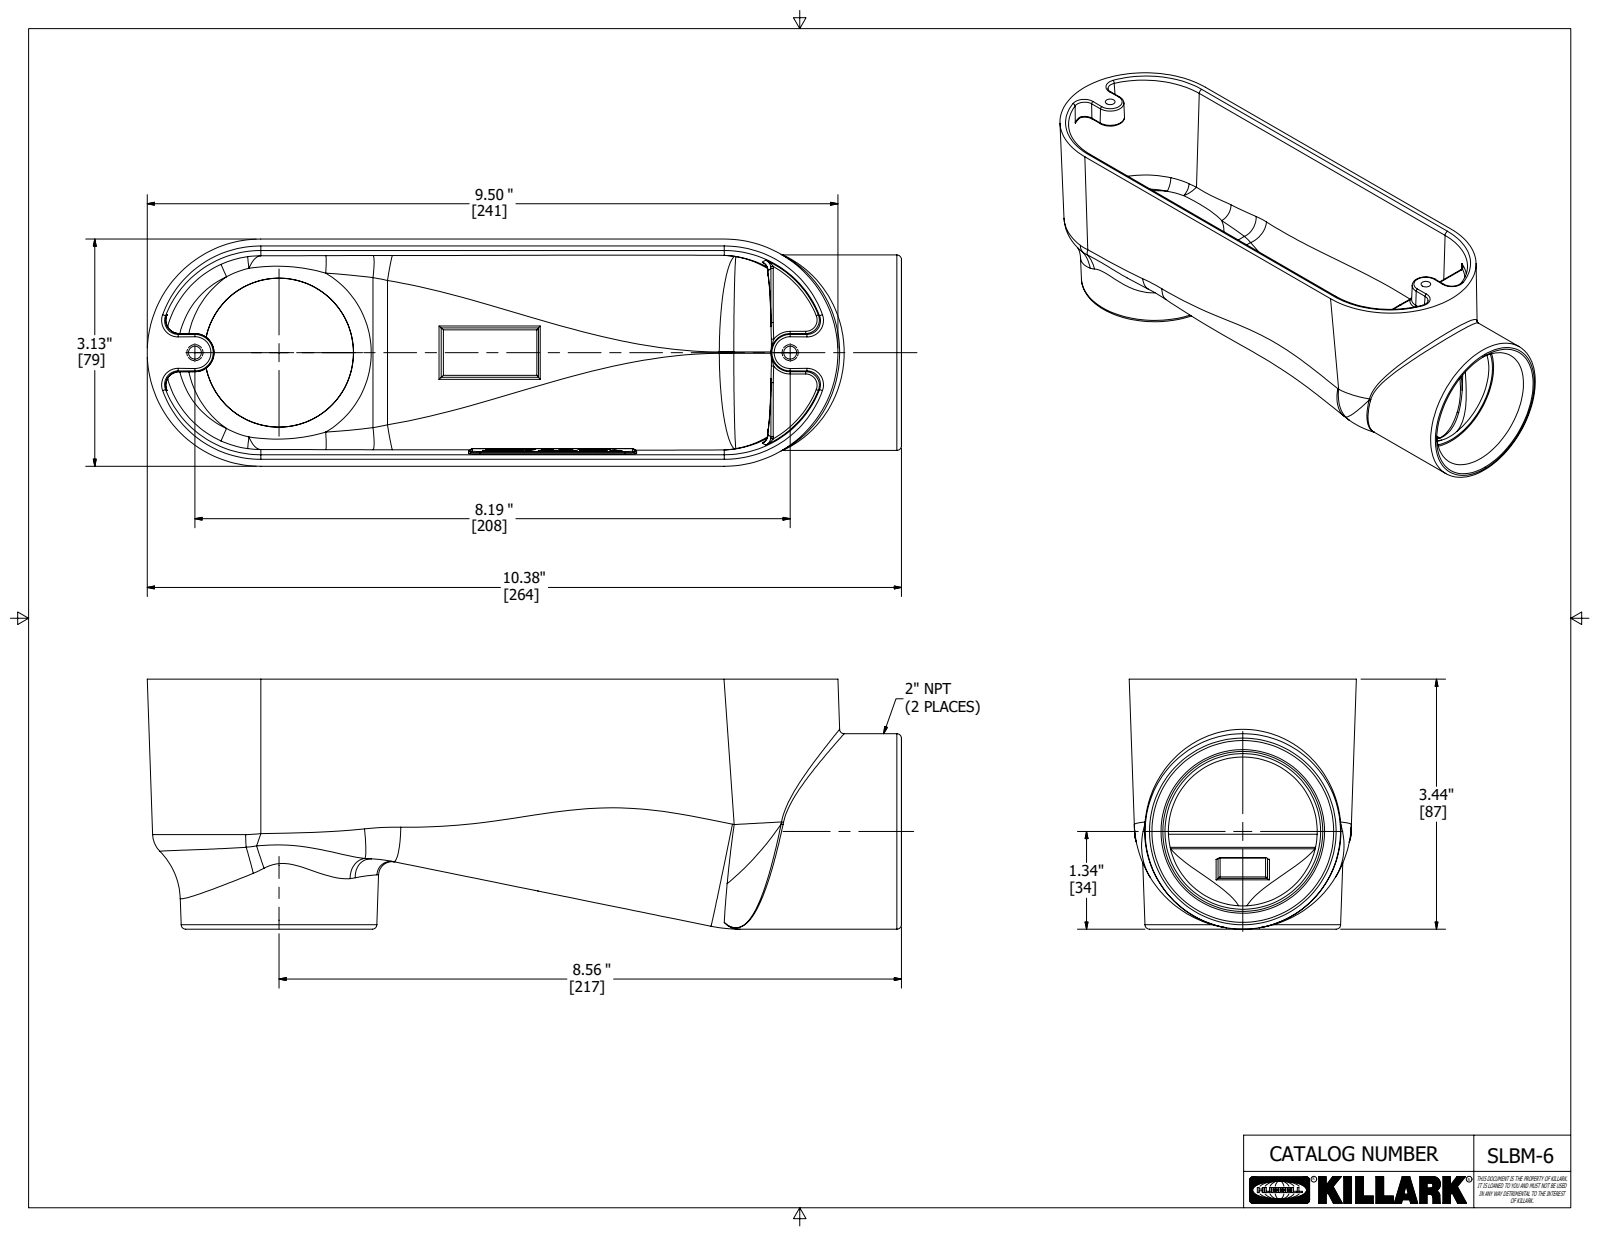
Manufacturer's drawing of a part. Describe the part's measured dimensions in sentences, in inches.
The part is named "0194842 -2". Its 3-D file was written by "Autodesk Inventor 2020 (AUTOMOTIVE_DESIGN)". It is 1 solid with 795 faces: 269 planar, 41 cylindrical and 485 other. Overall it measures 10.375 by 3.438 by 3.125 inches. Its volume is 16.7 cubic inches and its surface area 183.6 square inches. Round holes: 2 of diameter 0.177, 1 of diameter 2.047. Round bosses or shafts: 1 of diameter 2.687. Partial cylindrical surfaces (rounded edges, fillets, slot ends): 29 of radius 0.031, 2 of radius 1, 2 of radius 2, 1 of radius 0.25. The main face-to-face distances are 0.156, 0.154, 0.187, 0.031, 0.375, 0.187, 0.033, 1.938, 2.313, 0.031. The hole center spacings are 8.187.
